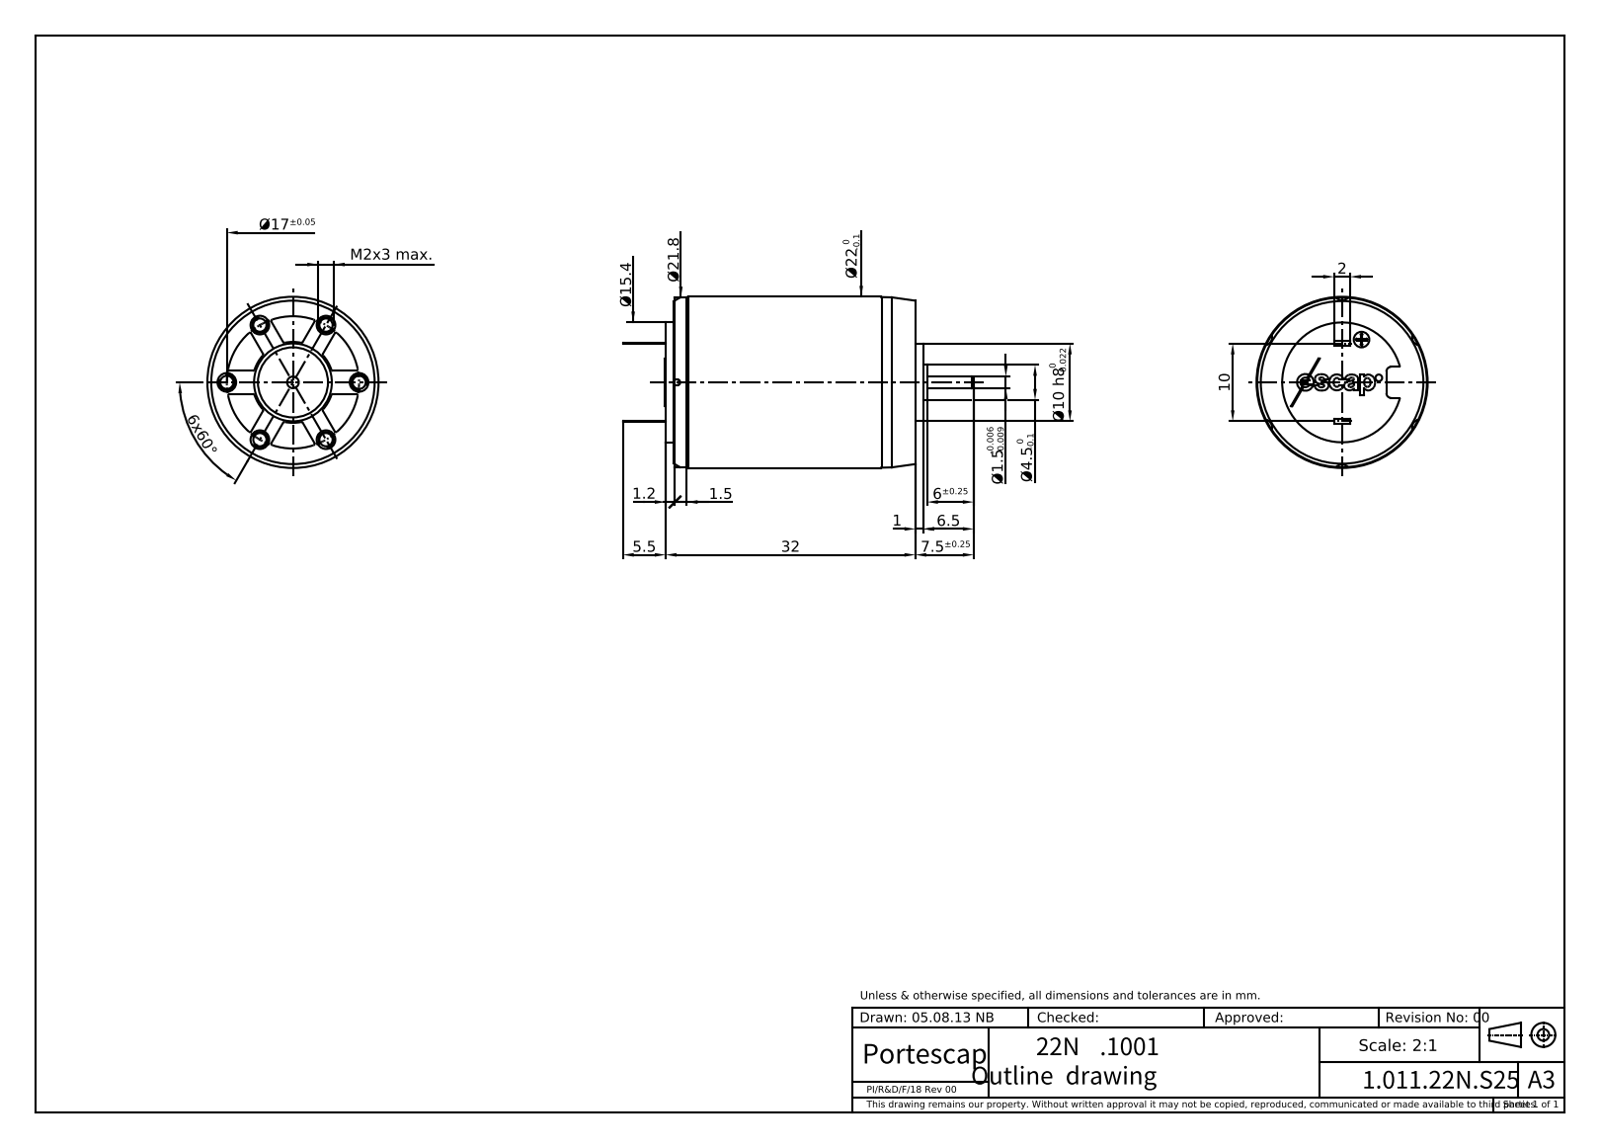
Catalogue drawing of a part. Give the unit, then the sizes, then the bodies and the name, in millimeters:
Units: millimetres
Overall size (bounding box): 45 × 22 × 22
Round holes (diameter × count): ⌀1.8 ×6, ⌀2.2 ×1, ⌀21 ×1, ⌀21.3 ×1
Round bosses / shafts (diameter × count): ⌀22 ×1, ⌀21.8 ×1, ⌀10 ×1, ⌀4.5 ×1, ⌀1.5 ×1
Partial cylindrical surfaces — rounded edges, fillets, slot ends (radius × count): R0.2 ×24, R0.5 ×4, R8.5 ×1
Main face-to-face distances: 27.6, 24.6, 3, 1, 28.6, 4, 1.34, 1.33, 10, 28.8
Hole centre spacings: 8.5, 14.72, 17
Volume: 10 277 mm³ · Surface area: 3 584 mm²
Bodies: 3 solids, 152 faces (49 planar, 67 cylindrical, 36 other)
Part name (STEP PRODUCT): 22N78_311_1001_ASM
STEP written by: PRO/ENGINEER BY PARAMETRIC TECHNOLOGY CORPORATION, 2014310 (CONFIG_CONTROL_DESIGN)
